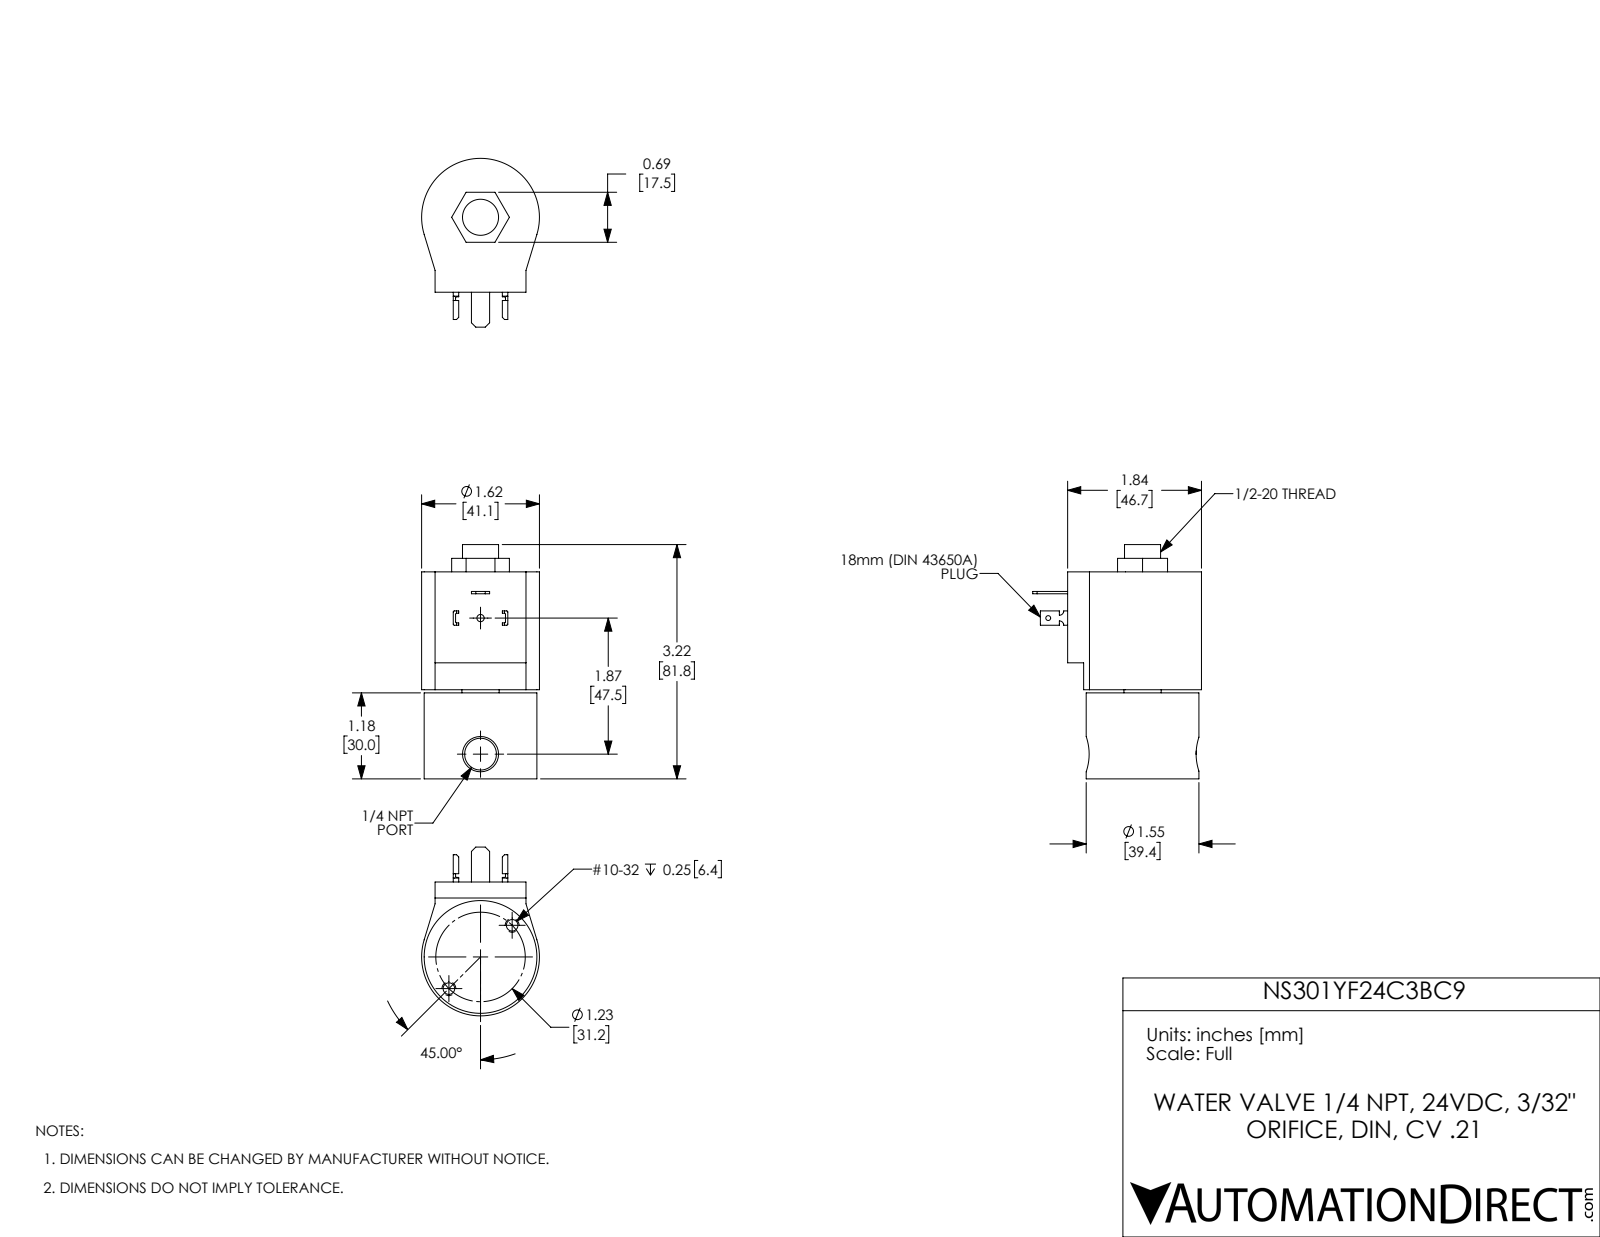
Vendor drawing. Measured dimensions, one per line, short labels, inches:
name: NS301YF16C3BC9
written by: SolidWorks 2017 (AUTOMOTIVE_DESIGN)
unit: in
bodies: 6 solids, 130 faces (73 planar, 49 cylindrical, 8 other)
size: 3.22 × 2.32 × 1.62
volume: 6.042 in³; area: 33.19 in²
holes: 2× ⌀0.159, 1× ⌀0.067, 1× ⌀0.1, 1× ⌀0.437, 1× ⌀0.496, 1× ⌀0.512, 1× ⌀1.155
bosses: 1× ⌀1.55
rounds: 8× R0.015, 2× R0.06, 1× R0.81
face distances: 2.845, 1.182, 1.663, 1.225, 0.043, 1.62, 1.287, 0.106, 0.062, 1.558
hole spacings: 0.615, 1.23, 1.87
